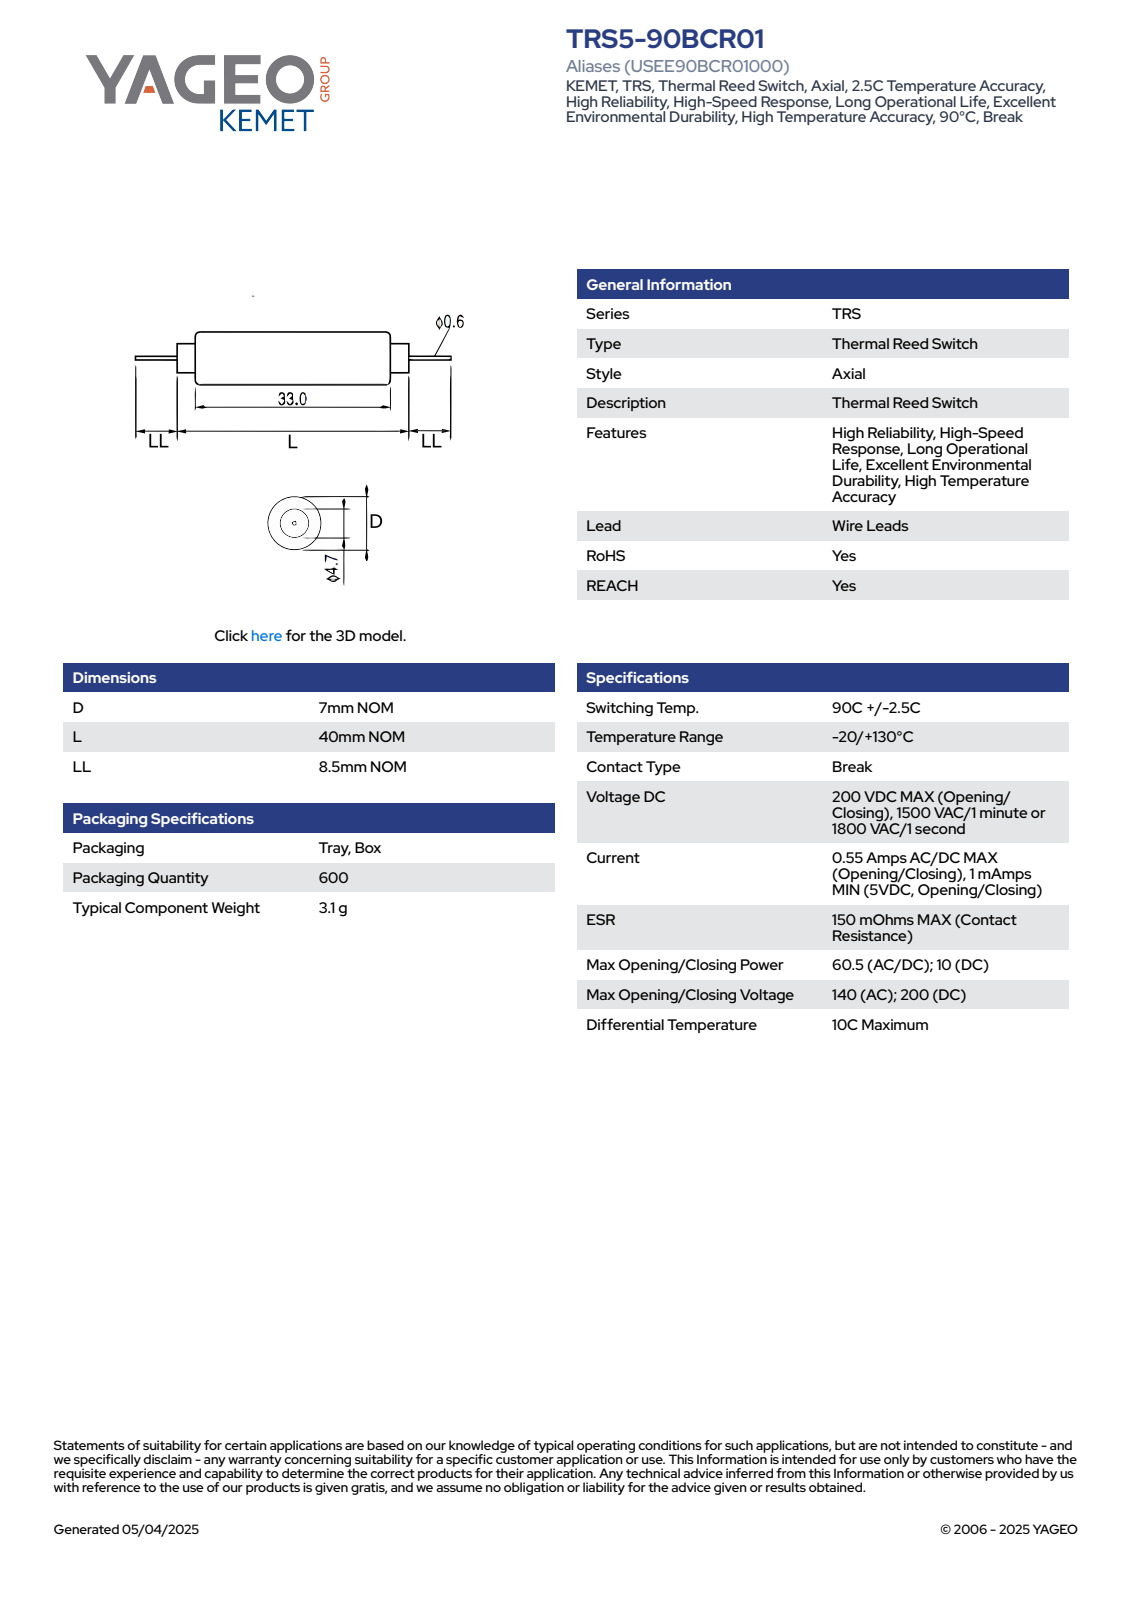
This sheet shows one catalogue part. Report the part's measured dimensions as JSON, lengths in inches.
{"part_name": "Default", "step_written_by": "SolidWorks 2014 (AUTOMOTIVE_DESIGN)", "units": "inches", "bodies": {"solids": 1, "faces": 91, "planar": 28, "cylindrical": 28, "other": 35}, "overall_size": [2.244, 0.276, 0.276], "volume_in3": 0.085, "surface_area_in2": 1.42, "round_bosses_or_shafts": [[0.276, 1], [0.185, 1], [0.024, 1]], "partial_cylinders_radius": [[0.137, 1]], "face_to_face_distances": [1.575, 0.138, 1.437, 1.299, 0.335, 0.472, 1.772, 1.909, 2.244]}
